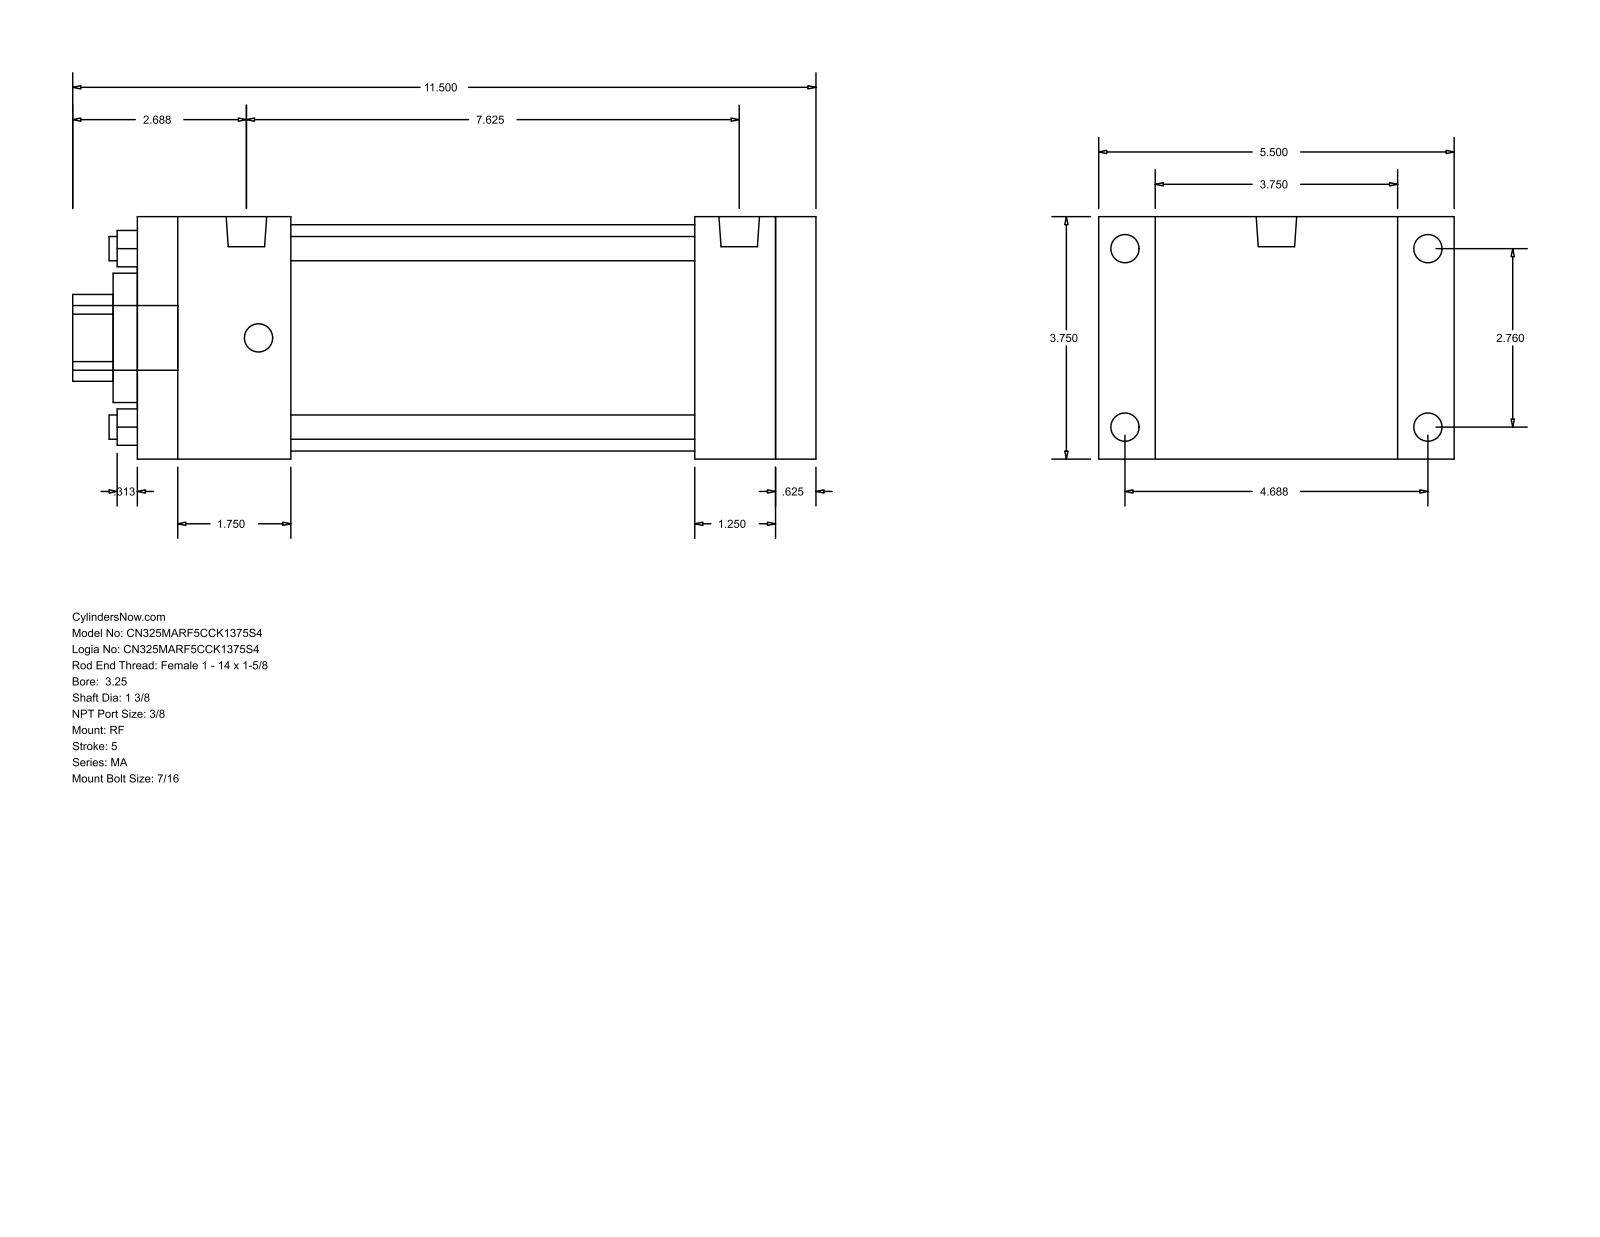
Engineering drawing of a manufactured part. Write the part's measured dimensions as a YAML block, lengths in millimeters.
part_name: "MA_RF__0325_1.375"
step_written_by: "GSSL Pune (CONFIG_CONTROL_DESIGN)"
units: millimeters
bodies: {solids: 0, faces: 92, planar: 64, cylindrical: 28, other: 0}
overall_size: [292.1, 139.7, 95.25]
round_holes:
  - {diameter: 9.53, count: 4}
  - {diameter: 34.92, count: 1}
  - {diameter: 50.8, count: 1}
  - {diameter: 88.9, count: 1}
round_bosses_or_shafts:
  - {diameter: 11.11, count: 8}
  - {diameter: 15.93, count: 2}
  - {diameter: 25.4, count: 1}
partial_cylinders:
  - {radius: 17.06, count: 1}
face_to_face_distances: [95.24, 266.7, 15.87, 250.83, 22.23, 117.47, 219.07, 31.76, 47.63, 60.32]
hole_center_spacings: [49.57, 70.1, 99.14]
